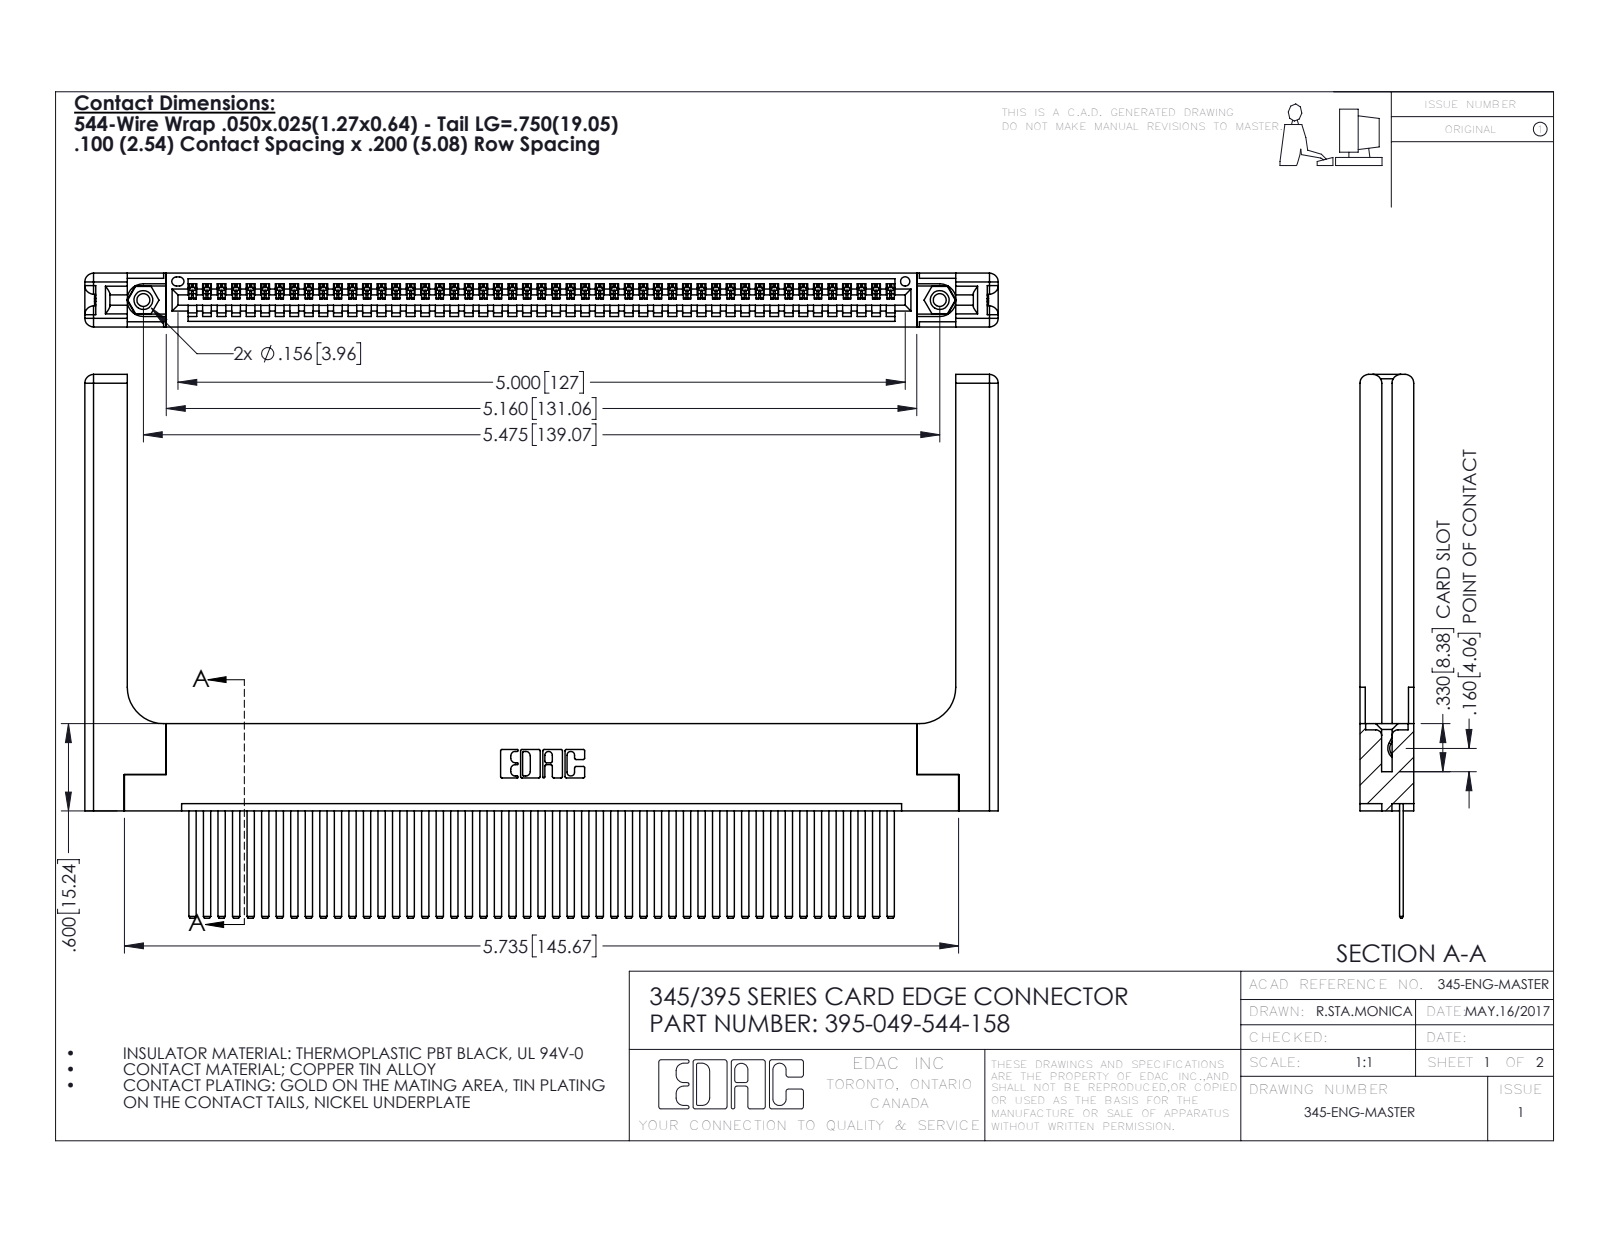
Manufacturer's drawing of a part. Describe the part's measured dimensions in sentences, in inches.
The part is named "395-049-544-158; 345-250-001_345-250-001-102; 345-292-001_345-293-144; 345 Part_Flush Mounting Lugs - 0.156 Dia-TH (+1 more)". Its 3-D file was written by "SolidWorks 2016 (CONFIG_CONTROL_DESIGN)". It is 54 solids with 2930 faces: 1992 planar, 878 cylindrical and 60 other. Overall it measures 6.279 by 3.737 by 0.37 inches. Its volume is 1.482 cubic inches and its surface area 43.5 square inches. Round holes: 2 of diameter 0.089, 2 of diameter 0.125, 2 of diameter 0.156, 1 of diameter 0.064. Round bosses or shafts: 2 of diameter 0.155. Partial cylindrical surfaces (rounded edges, fillets, slot ends): 98 of radius 0.006, 22 of radius 0.01, 16 of radius 0.06, 6 of radius 0.007, 6 of radius 0.031, 3 of radius 0.026, 2 of radius 0.03, 2 of radius 0.031. The main face-to-face distances are 0.072, 0.298, 0.37, 0.098, 0.272, 0.025, 0.2, 0.225, 0.148, 0.15. The hole center spacings are 0.27, 5.239, 5.475.
